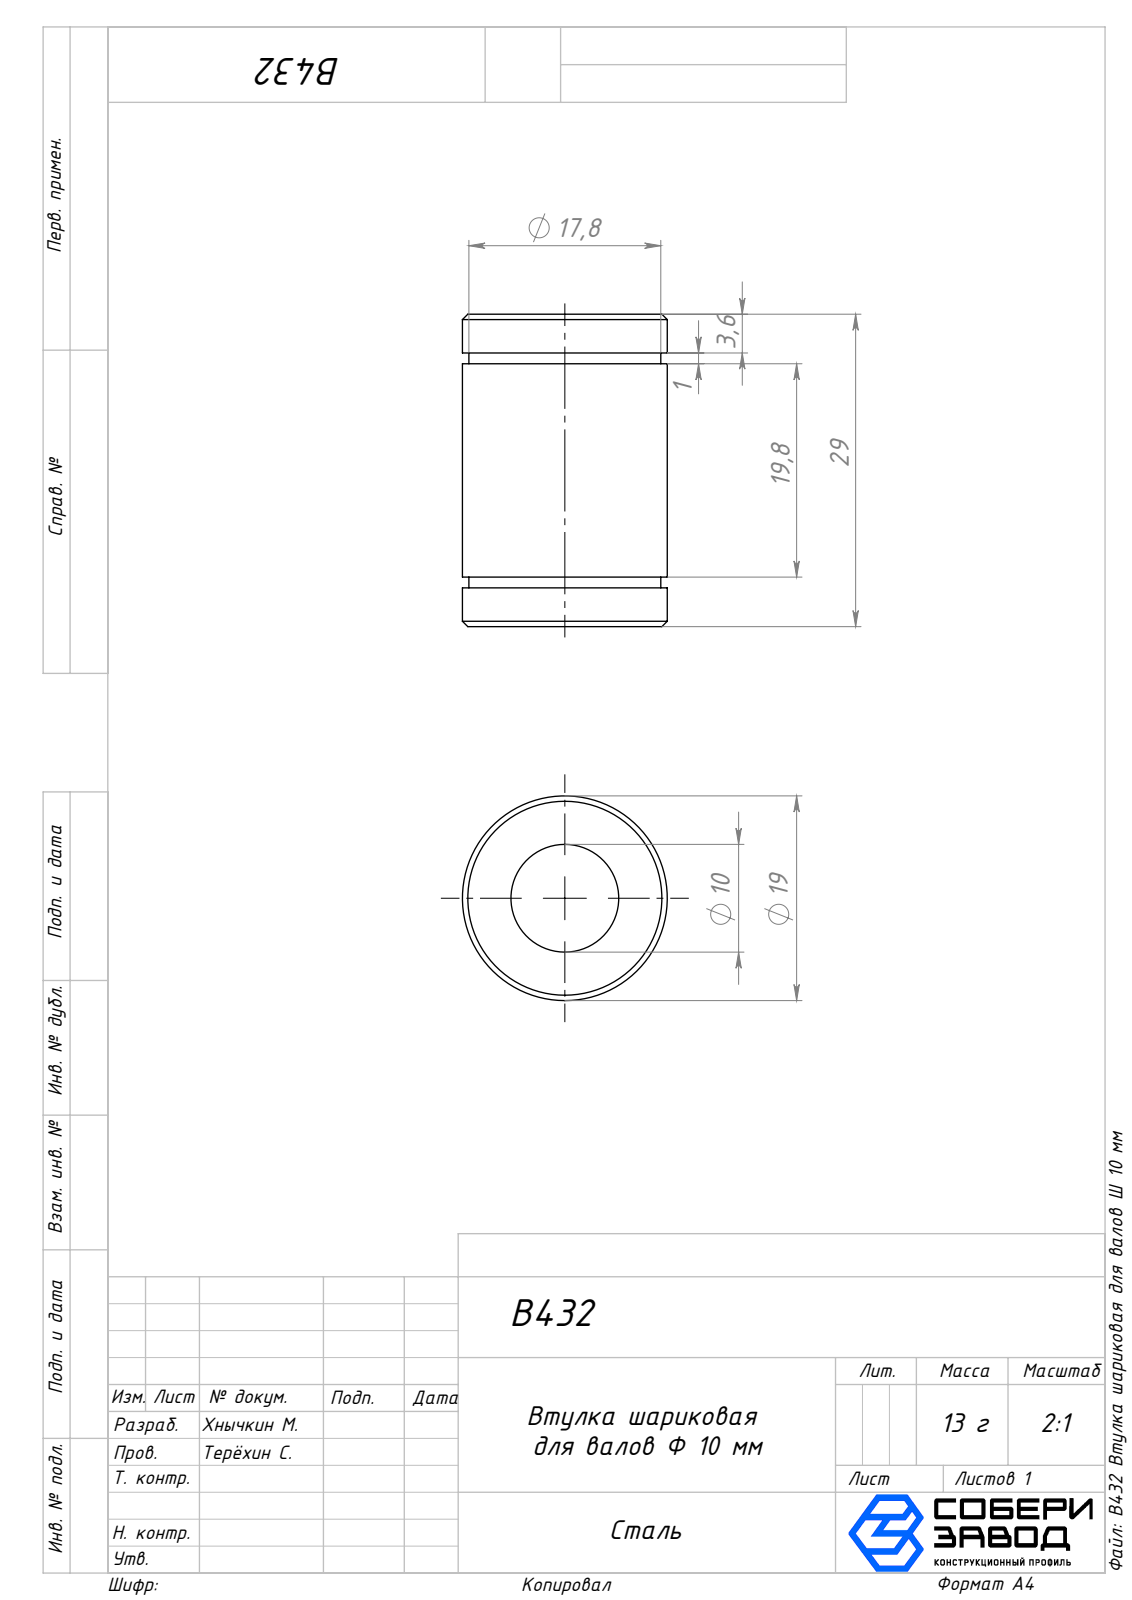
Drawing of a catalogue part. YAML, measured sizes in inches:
part_name: "B432 Втулка шариковая для валов Ø 10 мм"
step_written_by: "SolidWorks 2025 (AUTOMOTIVE_DESIGN)"
units: inches
bodies: {solids: 1, faces: 22, planar: 6, cylindrical: 12, other: 4}
overall_size: [1.142, 0.748, 0.748]
volume: 0.358
surface_area: 4.879
round_holes:
  - {diameter: 0.394, count: 1}
round_bosses_or_shafts:
  - {diameter: 0.748, count: 1}
  - {diameter: 0.701, count: 1}
face_to_face_distances: [1.142, 0.142, 1, 0.181, 0.961, 0.039, 0.819, 0.858, 0.78]
